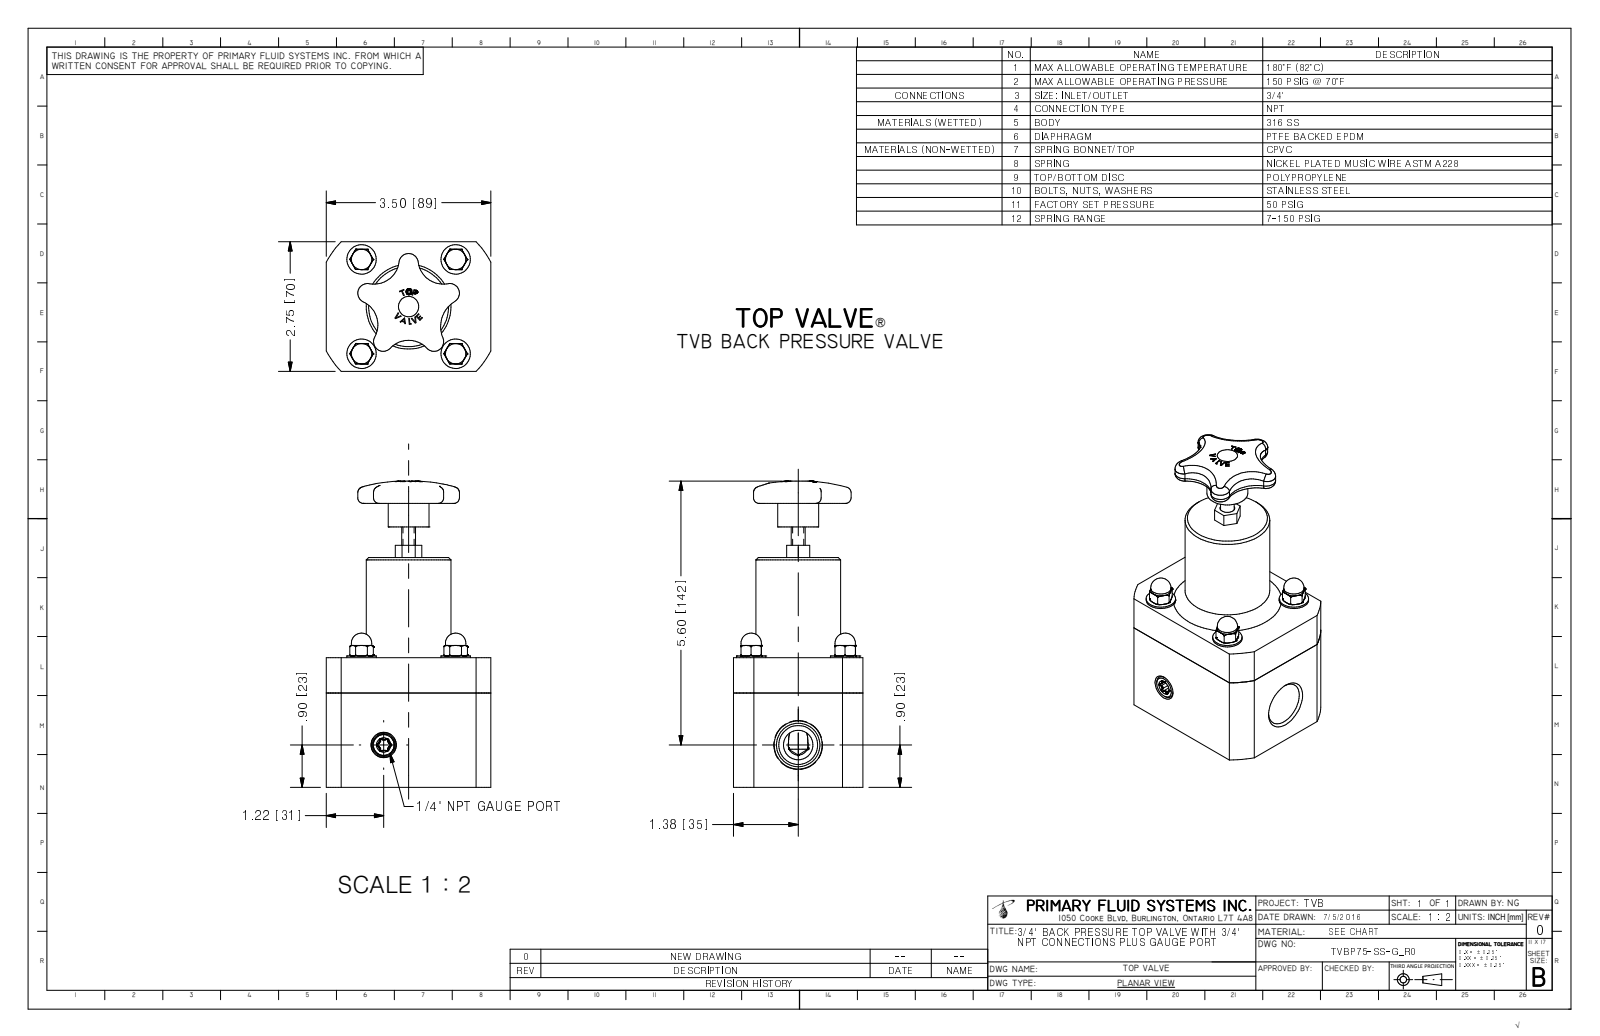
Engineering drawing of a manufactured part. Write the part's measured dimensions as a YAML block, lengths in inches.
part_name: "TVBP75-SS-G-R0"
step_written_by: "Autodesk Inventor 2009 (AUTOMOTIVE_DESIGN)"
units: inches
bodies: {solids: 1, faces: 359, planar: 152, cylindrical: 51, other: 156}
overall_size: [6.497, 3.5, 2.75]
volume: 31.72
surface_area: 82.67
round_holes:
  - {diameter: 0.175, count: 4}
  - {diameter: 0.922, count: 1}
round_bosses_or_shafts:
  - {diameter: 0.625, count: 4}
  - {diameter: 0.433, count: 4}
  - {diameter: 0.375, count: 4}
  - {diameter: 1.8, count: 1}
  - {diameter: 0.87, count: 1}
  - {diameter: 0.293, count: 1}
partial_cylinders:
  - {radius: 0.027, count: 6}
  - {radius: 0.085, count: 5}
  - {radius: 0.205, count: 5}
  - {radius: 0.536, count: 4}
  - {radius: 0.656, count: 4}
  - {radius: 0.625, count: 1}
  - {radius: 0.745, count: 1}
  - {radius: 1.988, count: 1}
face_to_face_distances: [2.75, 2.75, 3.5, 4.875, 2.125, 0.75, 2, 2.786, 0.036, 2.089]
hole_center_spacings: [2, 2.828]
